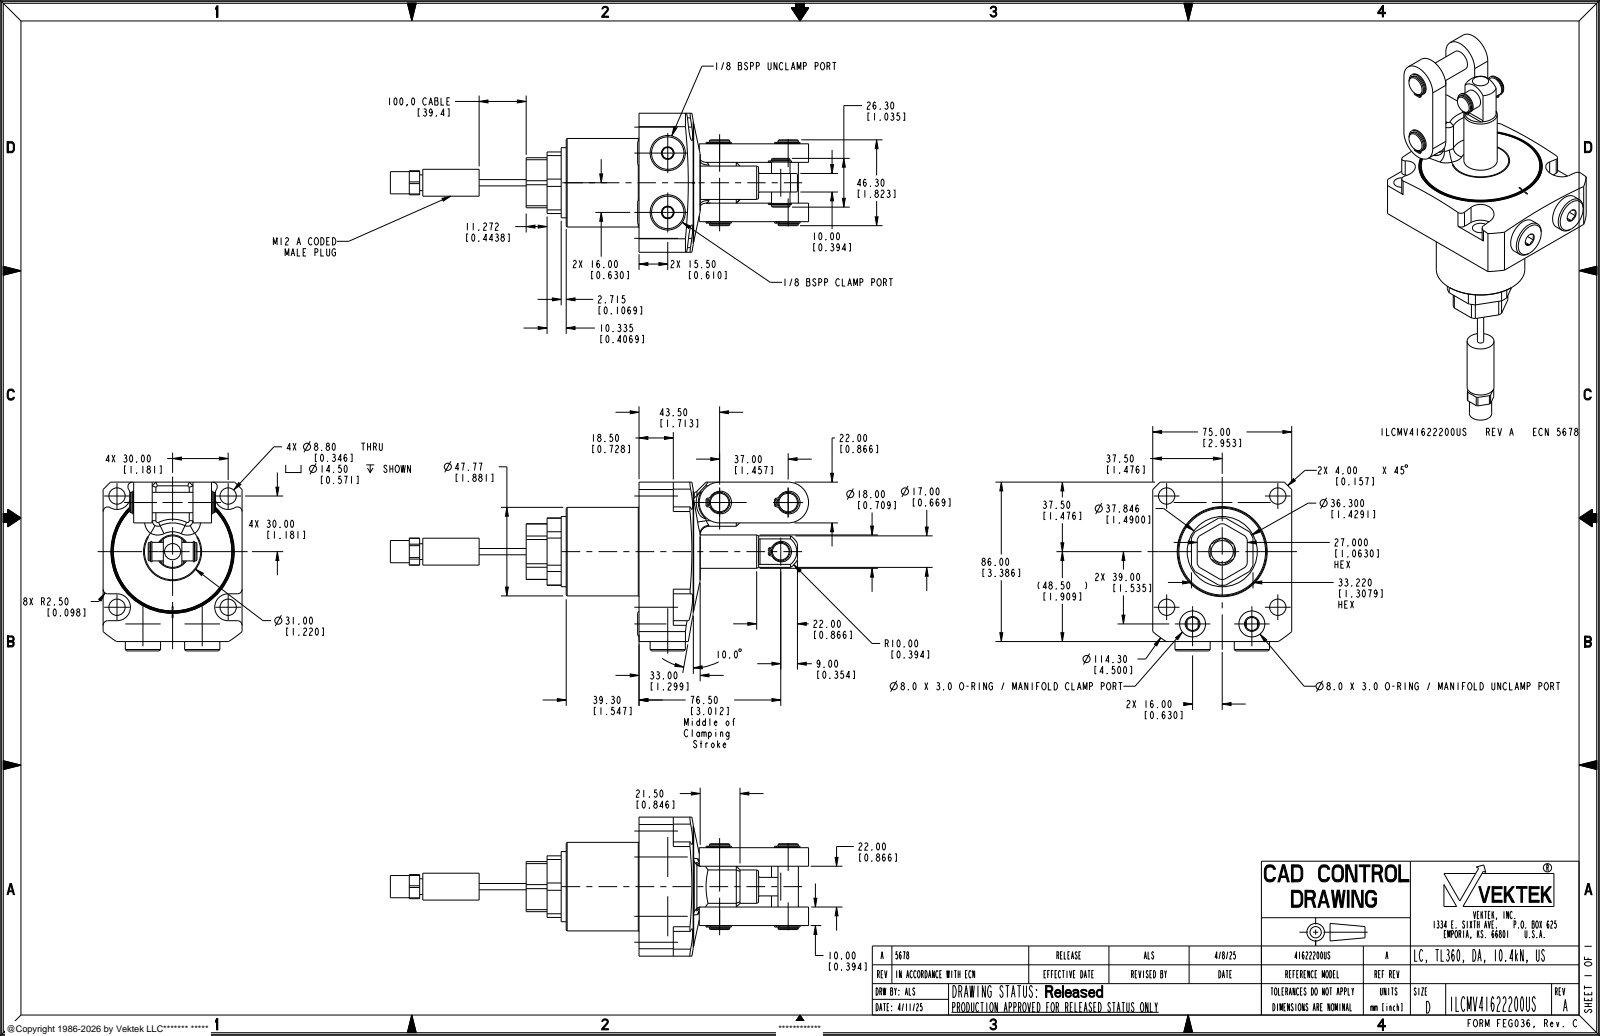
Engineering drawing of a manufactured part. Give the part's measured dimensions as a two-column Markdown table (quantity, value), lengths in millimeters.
| quantity | value |
| --- | --- |
| part name | ILCMV41622200_BODY_US; ILCMV41622200_LUG_US; ILCMV41622200US |
| STEP written by | CREO PARAMETRIC BY PTC INC, 2021164 (AUTOMOTIVE_DESIGN) |
| units | millimeters |
| bodies | 4 solids, 441 faces (164 planar, 189 cylindrical, 88 other) |
| overall size | 225.71 × 91.05 × 75 |
| volume | 324 314 mm³ |
| surface area | 61 350 mm² |
| round holes (diameter × count) | 1.04 × 6, 8.8 × 4, 7.04 × 2, 8.84 × 2, 14 × 2, 64.03 × 1 |
| round bosses / shafts (diameter × count) | 19 × 2, 12.23 × 2, 11 × 2, 10.46 × 2, 9.73 × 2, 8 × 2, 63.93 × 1, 47.77 × 1 |
| partial cylindrical surfaces (radius × count) | 2.5 × 8, 1.04 × 6, 0.8 × 4, 1.57 × 4, 7.25 × 4, 1.46 × 2, 3 × 2, 11 × 2 |
| main face-to-face distances | 19, 16.5, 58.5, 10, 75, 22, 26.5, 48.5, 32, 86 |
| hole center spacings | 42.43, 60, 2.6, 16.64, 32, 37, 37.09, 42.15 |
